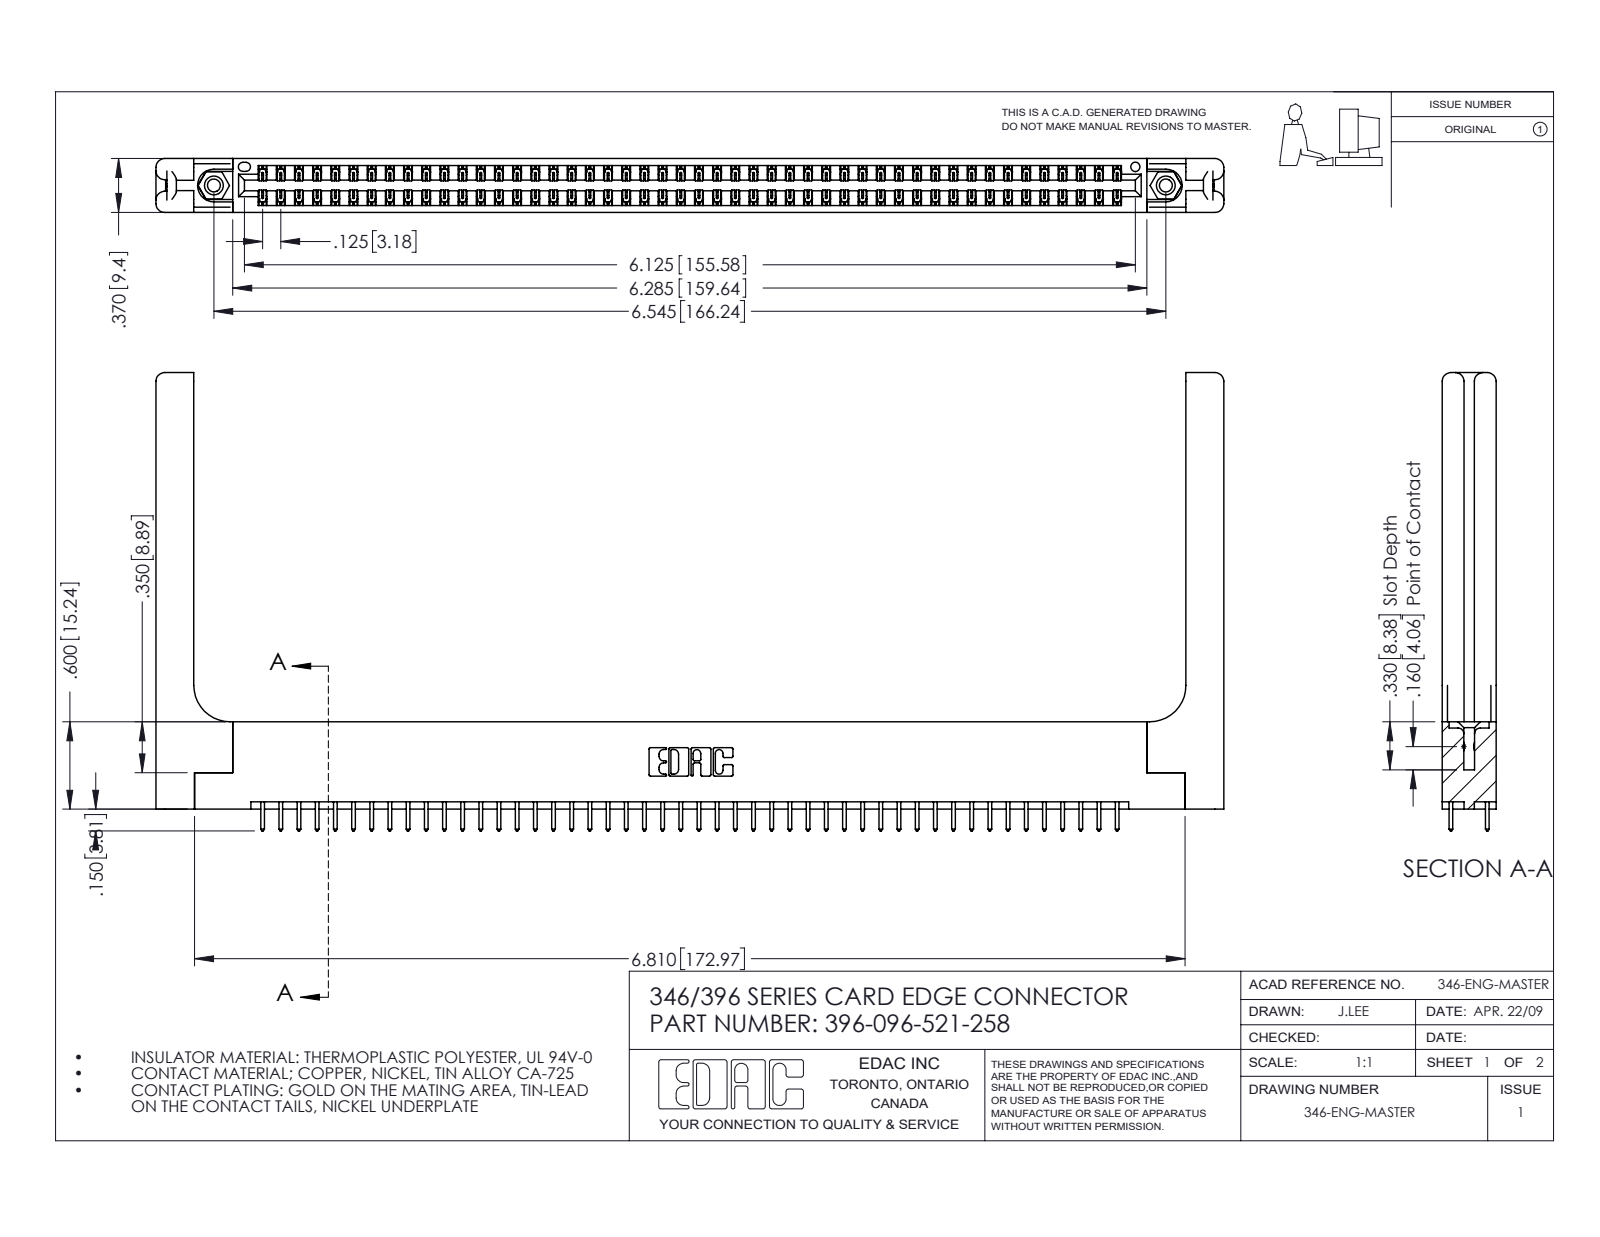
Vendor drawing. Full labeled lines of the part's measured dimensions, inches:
Part name (STEP PRODUCT): 396-096-521-258; 346-220-058_345-220-058; 345-292-001_345-293-121; 345-250-001_345-250-001-102 (+1 more)
STEP written by: SolidWorks 2016 (CONFIG_CONTROL_DESIGN)
Units: inches
Bodies: 101 solids, 5370 faces (3584 planar, 1726 cylindrical, 60 other)
Overall size (bounding box): 7.341 × 3.15 × 0.37
Volume: 1.567 in³ · Surface area: 46.2 in²
Round holes (diameter × count): ⌀0.089 ×2, ⌀0.125 ×2, ⌀0.156 ×2, ⌀0.064 ×1
Round bosses / shafts (diameter × count): ⌀0.155 ×2
Partial cylindrical surfaces — rounded edges, fillets, slot ends (radius × count): R0.006 ×144, R0.01 ×96, R0.01 ×22, R0.06 ×16, R0.007 ×6, R0.031 ×6, R0.026 ×3, R0.014 ×2
Main face-to-face distances: 0.048, 0.322, 0.37, 0.072, 0.25, 0.148, 0.15, 0.025, 0.298, 0.275
Hole centre spacings: 0.246, 6.336, 6.545
